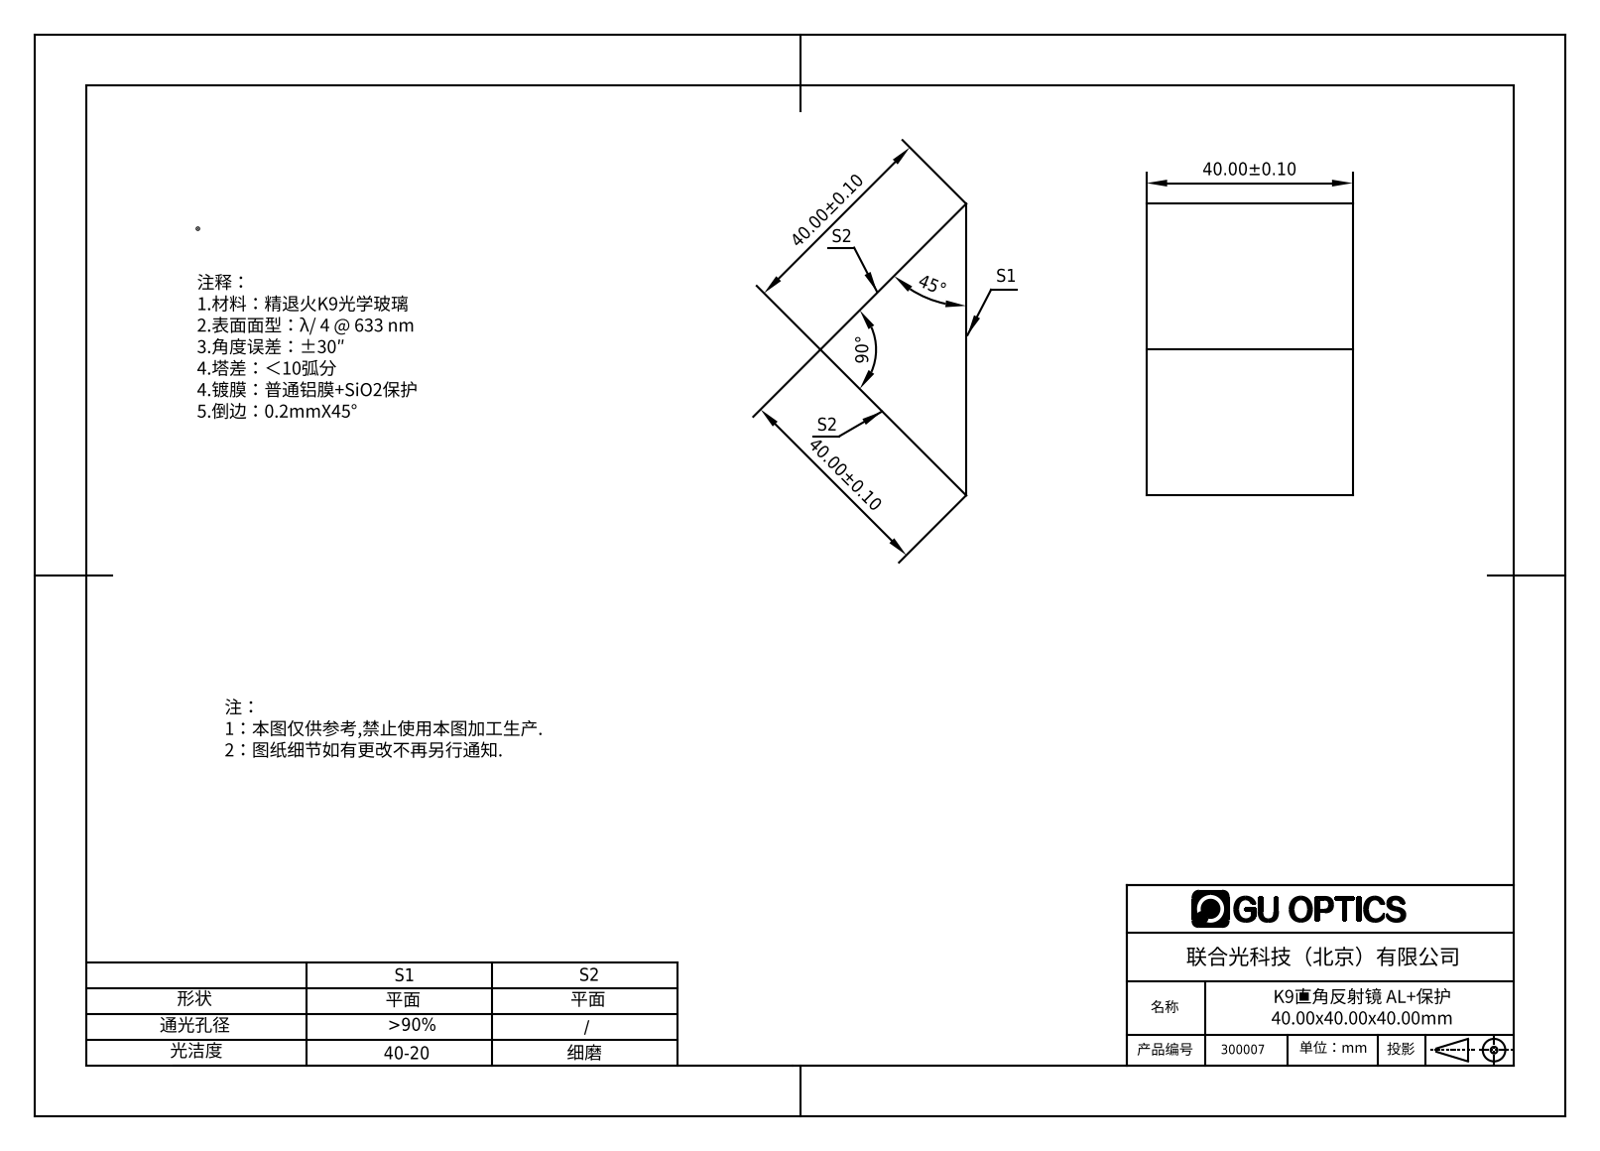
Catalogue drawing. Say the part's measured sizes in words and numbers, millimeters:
The part is named "300007". Its 3-D file was written by "SolidWorks 2016 (AUTOMOTIVE_DESIGN)". It is 1 solid with 5 faces: 5 planar, 0 cylindrical and 0 other. Overall it measures 56.57 by 40 by 28.28 millimeters. Its volume is 32 000 cubic millimeters and its surface area 7 063 square millimeters. The main face-to-face distances are 40.
